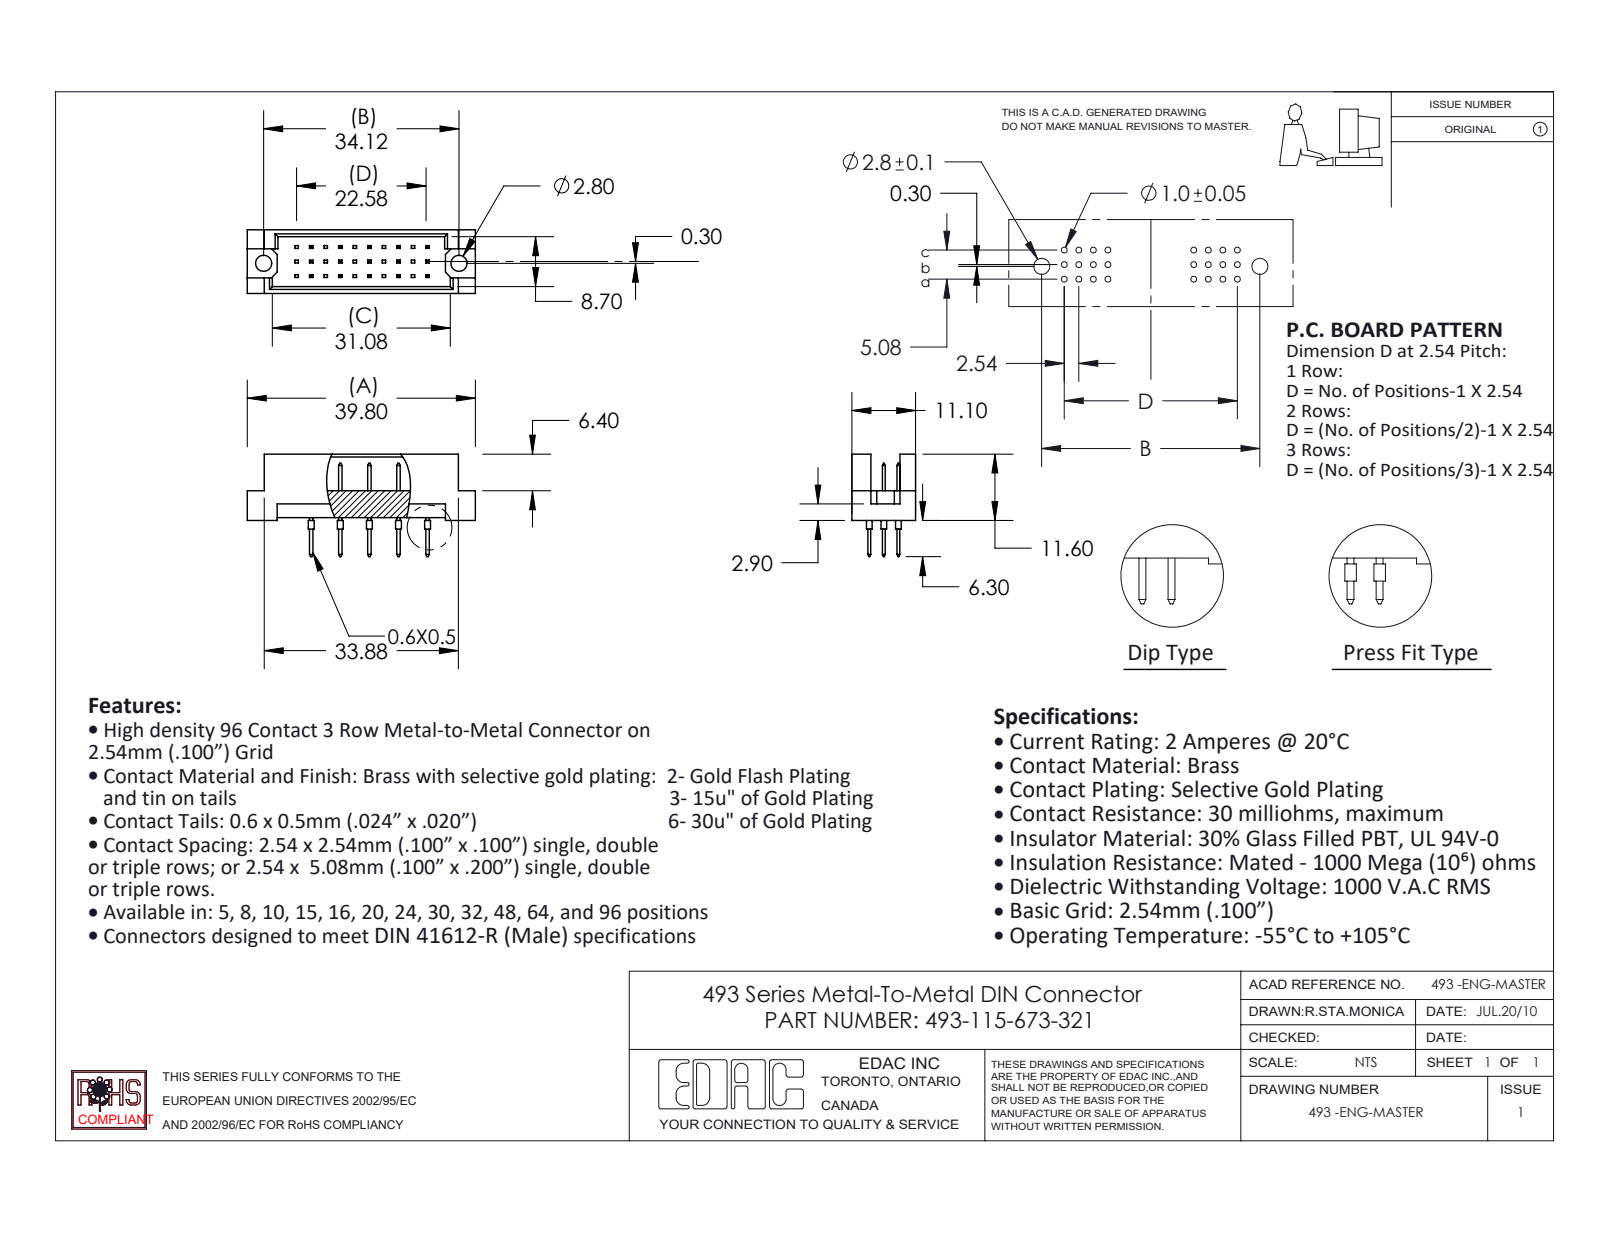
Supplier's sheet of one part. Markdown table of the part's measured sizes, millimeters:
| quantity | value |
| --- | --- |
| part name | 493-290_73; 493 Part_30; 493-115-673-321 |
| STEP written by | SolidWorks 2020 (CONFIG_CONTROL_DESIGN) |
| units | millimeters |
| bodies | 16 solids, 502 faces (468 planar, 34 cylindrical, 0 other) |
| overall size | 39.8 × 17.9 × 11.1 |
| volume | 2 456 mm³ |
| surface area | 3 306 mm² |
| round holes (diameter × count) | 2.8 × 2 |
| round bosses / shafts (diameter × count) | 1 × 15 |
| main face-to-face distances | 1.2, 9.9, 5.08, 11.1, 0.5, 8.7, 2.54, 4.7, 10.16, 2.76 |
| hole center spacings | 34.12 |
